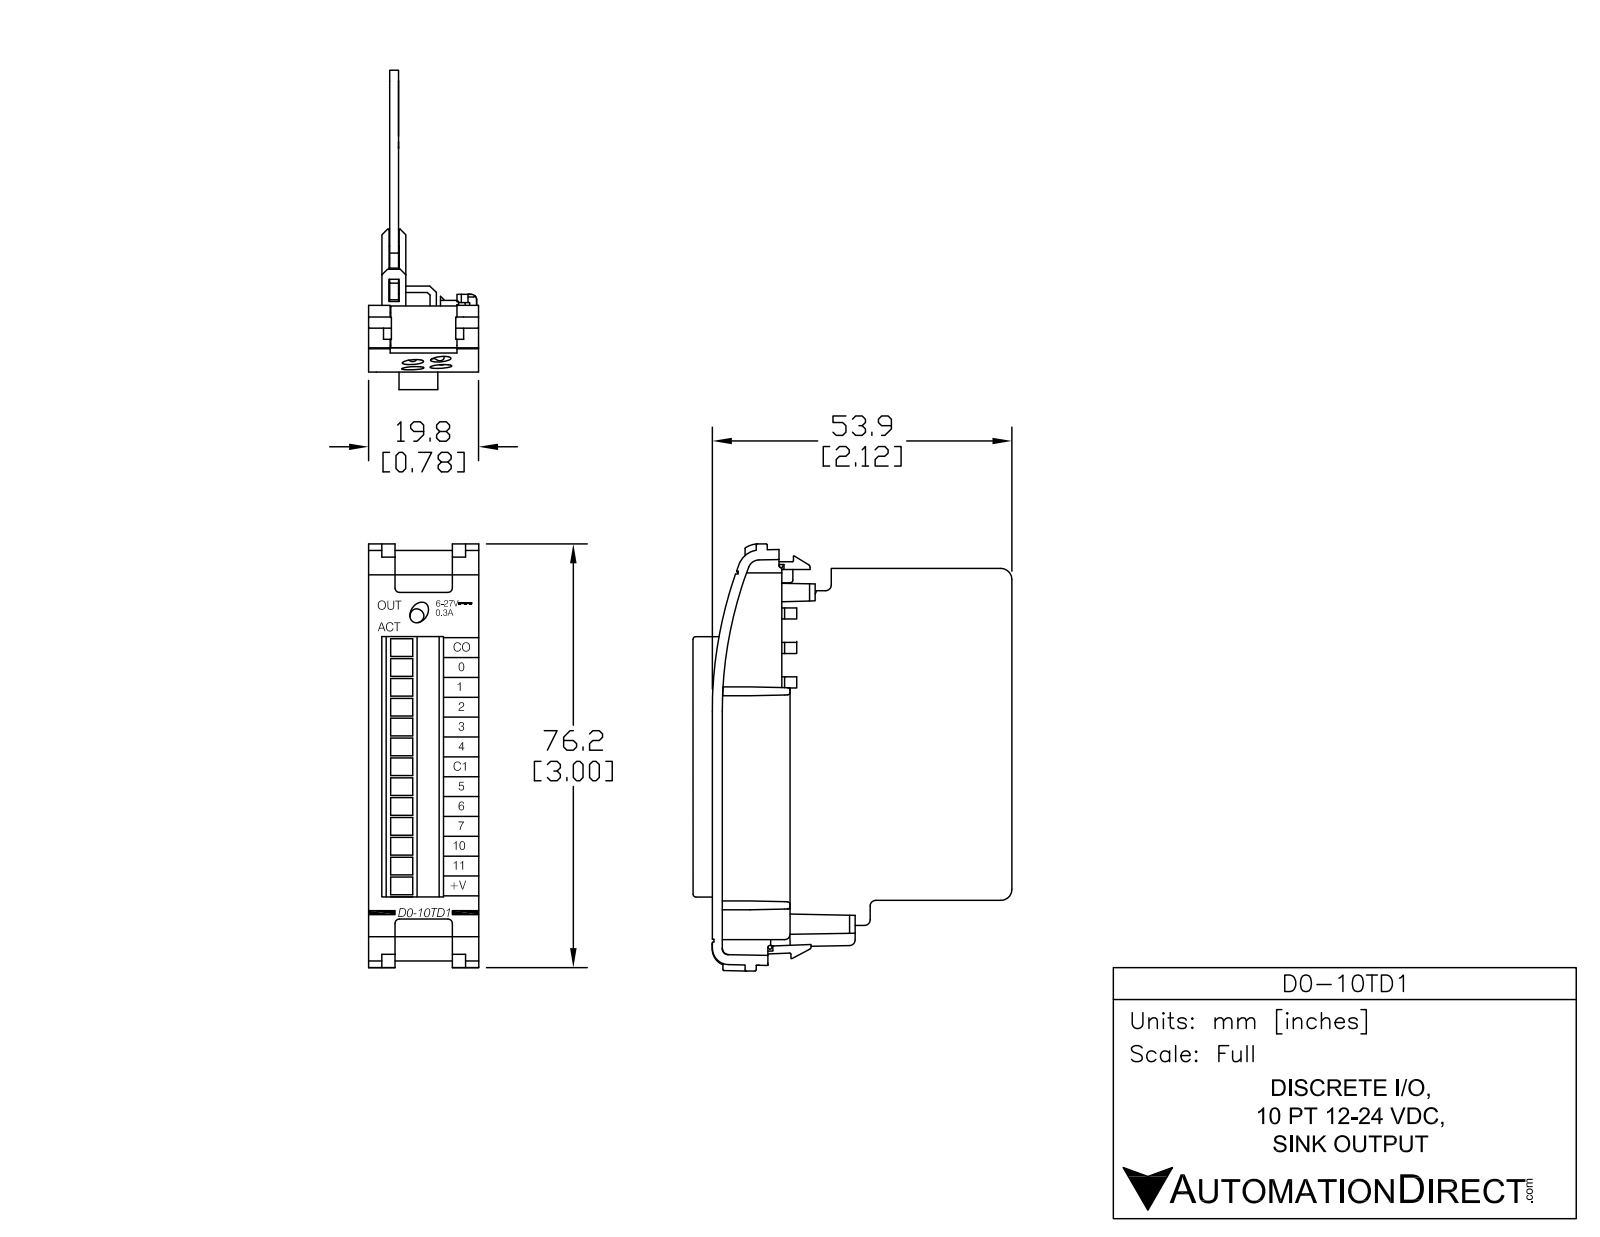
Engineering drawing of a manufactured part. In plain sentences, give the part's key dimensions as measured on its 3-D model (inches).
The part is named "D0-10TD1". Its 3-D file was written by "SolidWorks 2009 (AUTOMOTIVE_DESIGN)". It is 2 solids with 351 faces: 279 planar, 38 cylindrical and 34 other. Overall it measures 3.08 by 2.542 by 0.826 inches. Its volume is 0.753 cubic inches and its surface area 24.14 square inches. Round bosses or shafts: 1 of diameter 0.08. Partial cylindrical surfaces (rounded edges, fillets, slot ends): 4 of radius 0.005, 3 of radius 0.02, 3 of radius 0.035, 2 of radius 0.025, 1 of radius 0.01, 1 of radius 0.065, 1 of radius 0.07, 1 of radius 0.1. The main face-to-face distances are 0.063, 0.05, 0.631, 0.075, 0.113, 0.581, 0.518, 0.681, 0.568, 0.06.
